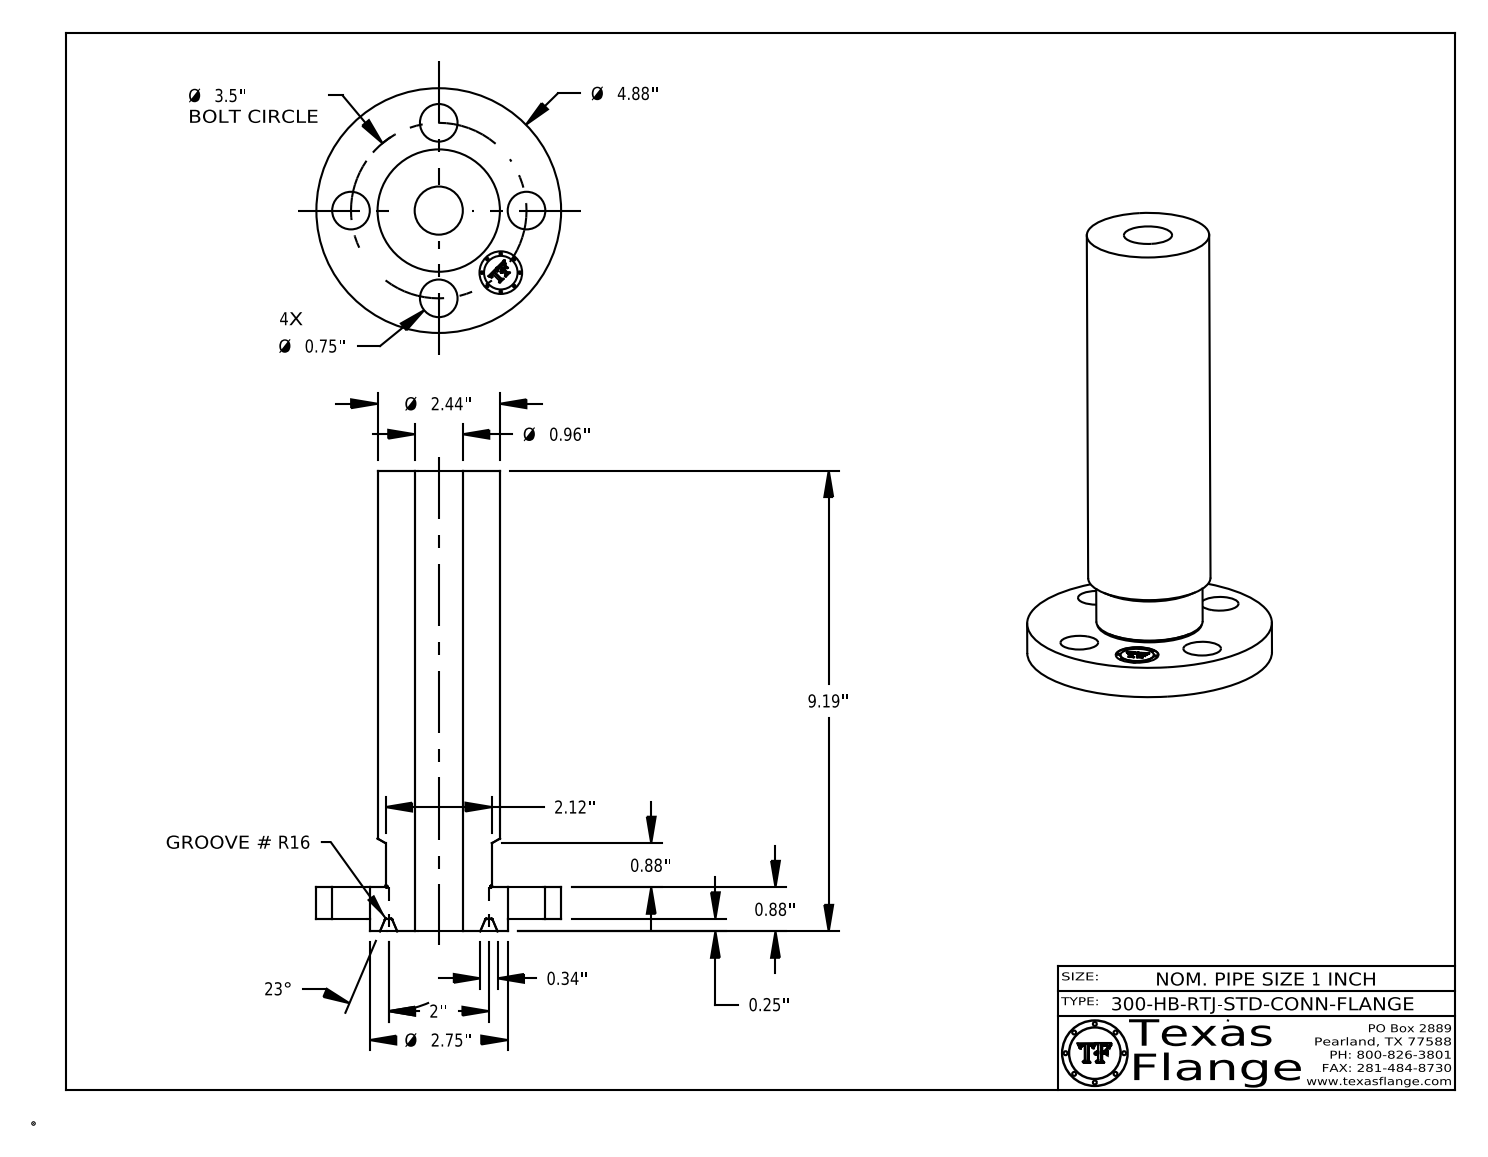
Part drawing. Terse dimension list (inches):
name: 1-300-HB-RTJ-STD-CONN-FLANGE
written by: CATIA V5 STEP AP214 (AUTOMOTIVE_DESIGN)
unit: in
bodies: 1 solid, 423 faces (371 planar, 38 cylindrical, 14 other)
size: 9.188 × 4.88 × 4.88
volume: 42.88 in³; area: 144.7 in²
holes: 4× ⌀0.75, 1× ⌀0.85, 1× ⌀0.96
bosses: 8× ⌀0.051, 1× ⌀4.88, 1× ⌀2.75, 1× ⌀2.44, 1× ⌀2.12, 1× ⌀0.67
face distances: 0.628, 8.937, 8.31, 0.25, 0.878, 9.187, 0.872, 0.622, 8.315, 0.016
hole spacings: 1.75, 2.475, 1.339, 3.233, 3.5
